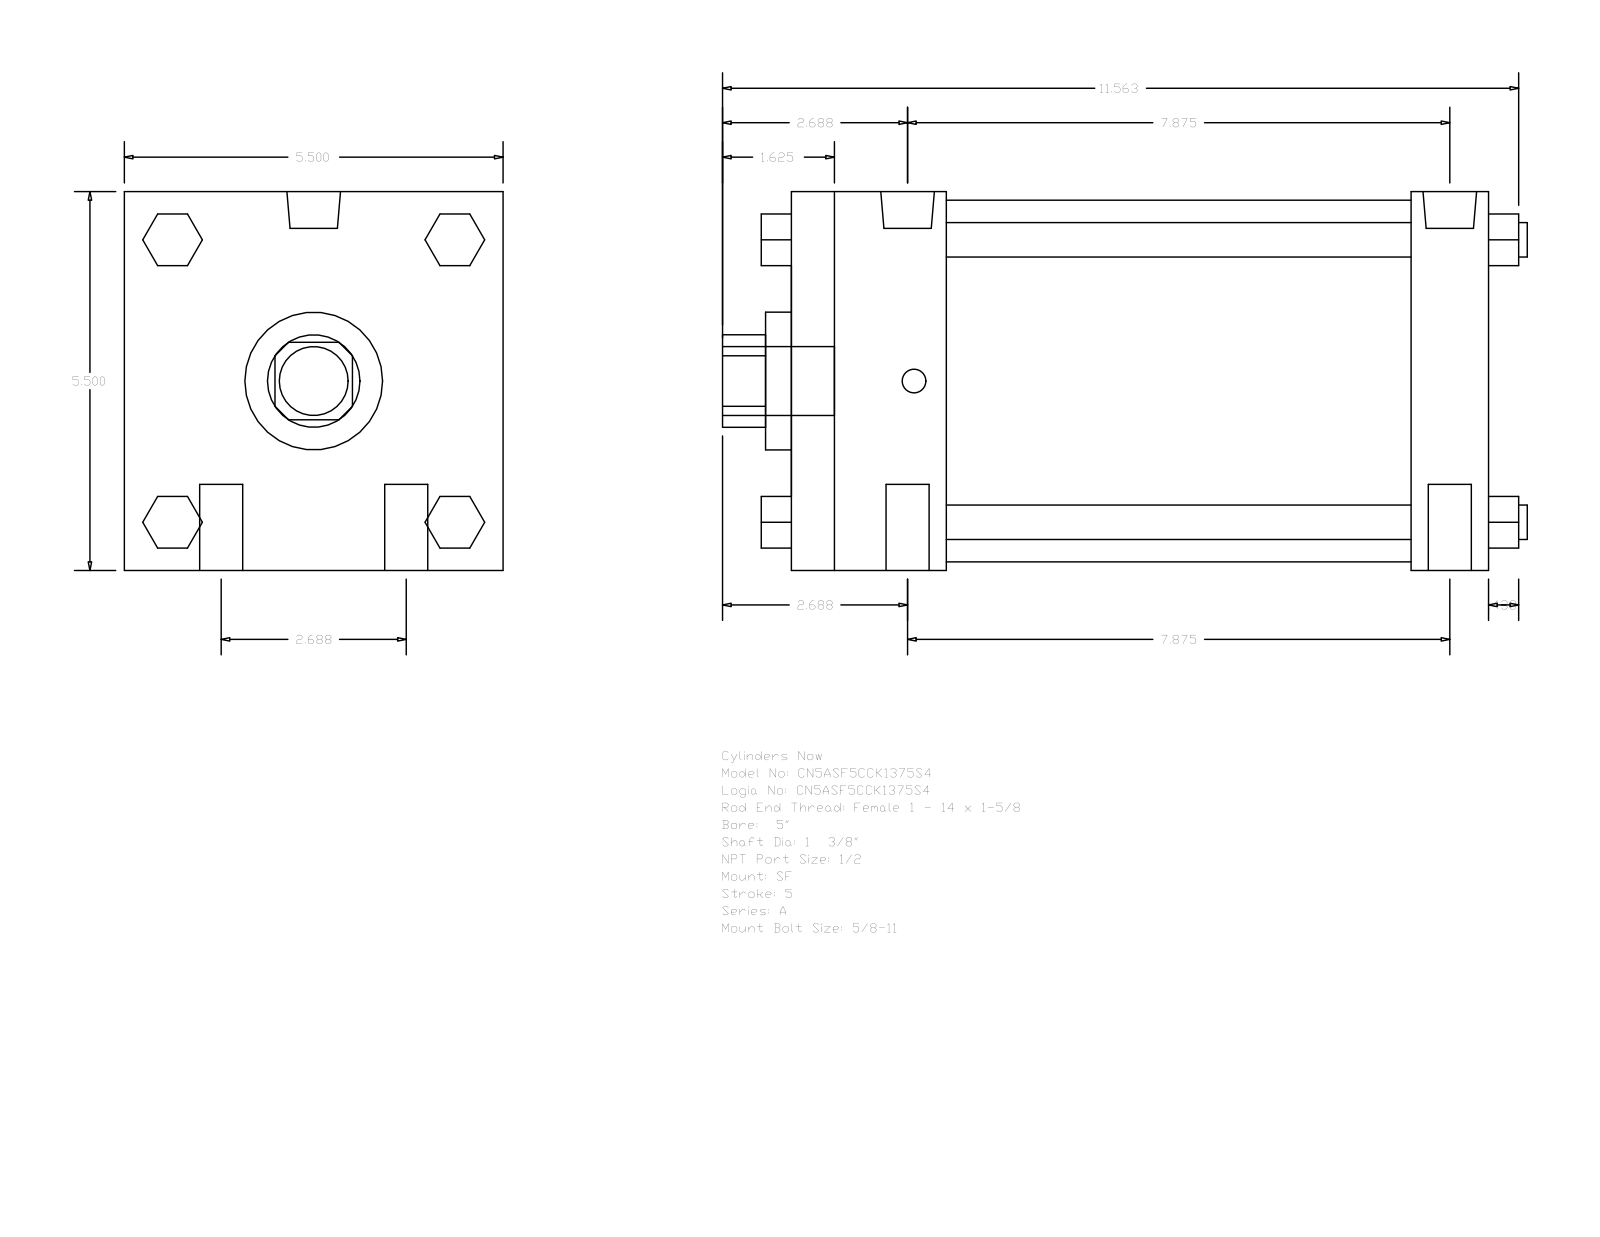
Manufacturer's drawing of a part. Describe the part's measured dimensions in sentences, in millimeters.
The part is named "A_SF__0500_1.375". Its 3-D file was written by "GSSL Pune (CONFIG_CONTROL_DESIGN)". It is 0 solids with 124 faces: 94 planar, 30 cylindrical and 0 other. Overall it measures 296.86 by 139.7 by 139.7 millimeters. Round holes: 1 of diameter 34.92, 1 of diameter 50.8, 1 of diameter 133.35. Round bosses or shafts: 4 of diameter 15.88, 4 of diameter 12.7, 2 of diameter 19.77, 2 of diameter 8.73, 1 of diameter 25.4. Partial cylindrical surfaces (rounded edges, fillets, slot ends): 1 of radius 17.06. The main face-to-face distances are 139.7, 257.17, 28.57, 57.15, 228.6, 171.45, 200.02, 19.05, 52.07, 90.18.
